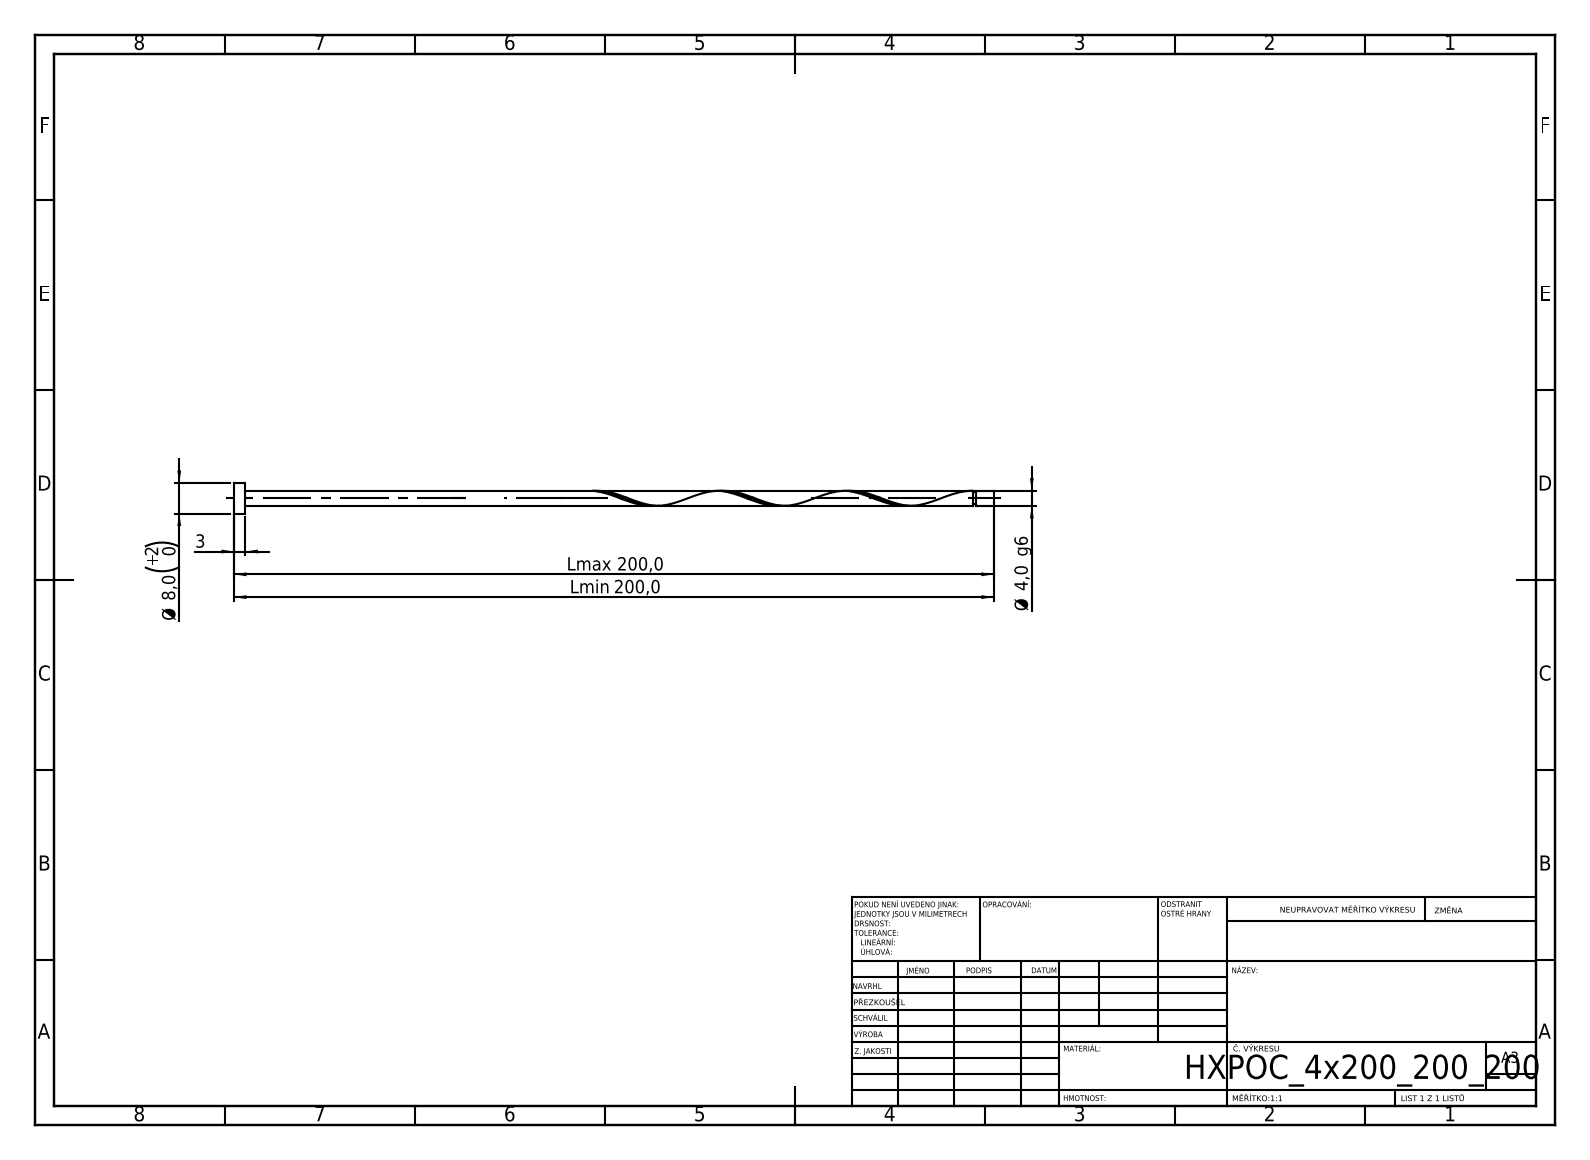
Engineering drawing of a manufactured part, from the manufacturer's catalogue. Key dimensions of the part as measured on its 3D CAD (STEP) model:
STEP written by: SolidWorks 2019 (CONFIG_CONTROL_DESIGN)
Units: millimetres
Bodies: 1 solid, 21 faces (6 planar, 14 cylindrical, 1 other)
Overall size (bounding box): 200 × 8 × 8
Volume: 2 599 mm³ · Surface area: 2 700 mm²
Round bosses / shafts (diameter × count): ⌀8 ×1, ⌀4 ×1, ⌀3.2 ×1
Main face-to-face distances: 3, 200, 197, 195.21, 192.21, 4.79, 194.41, 191.41, 0.8, 5.59
